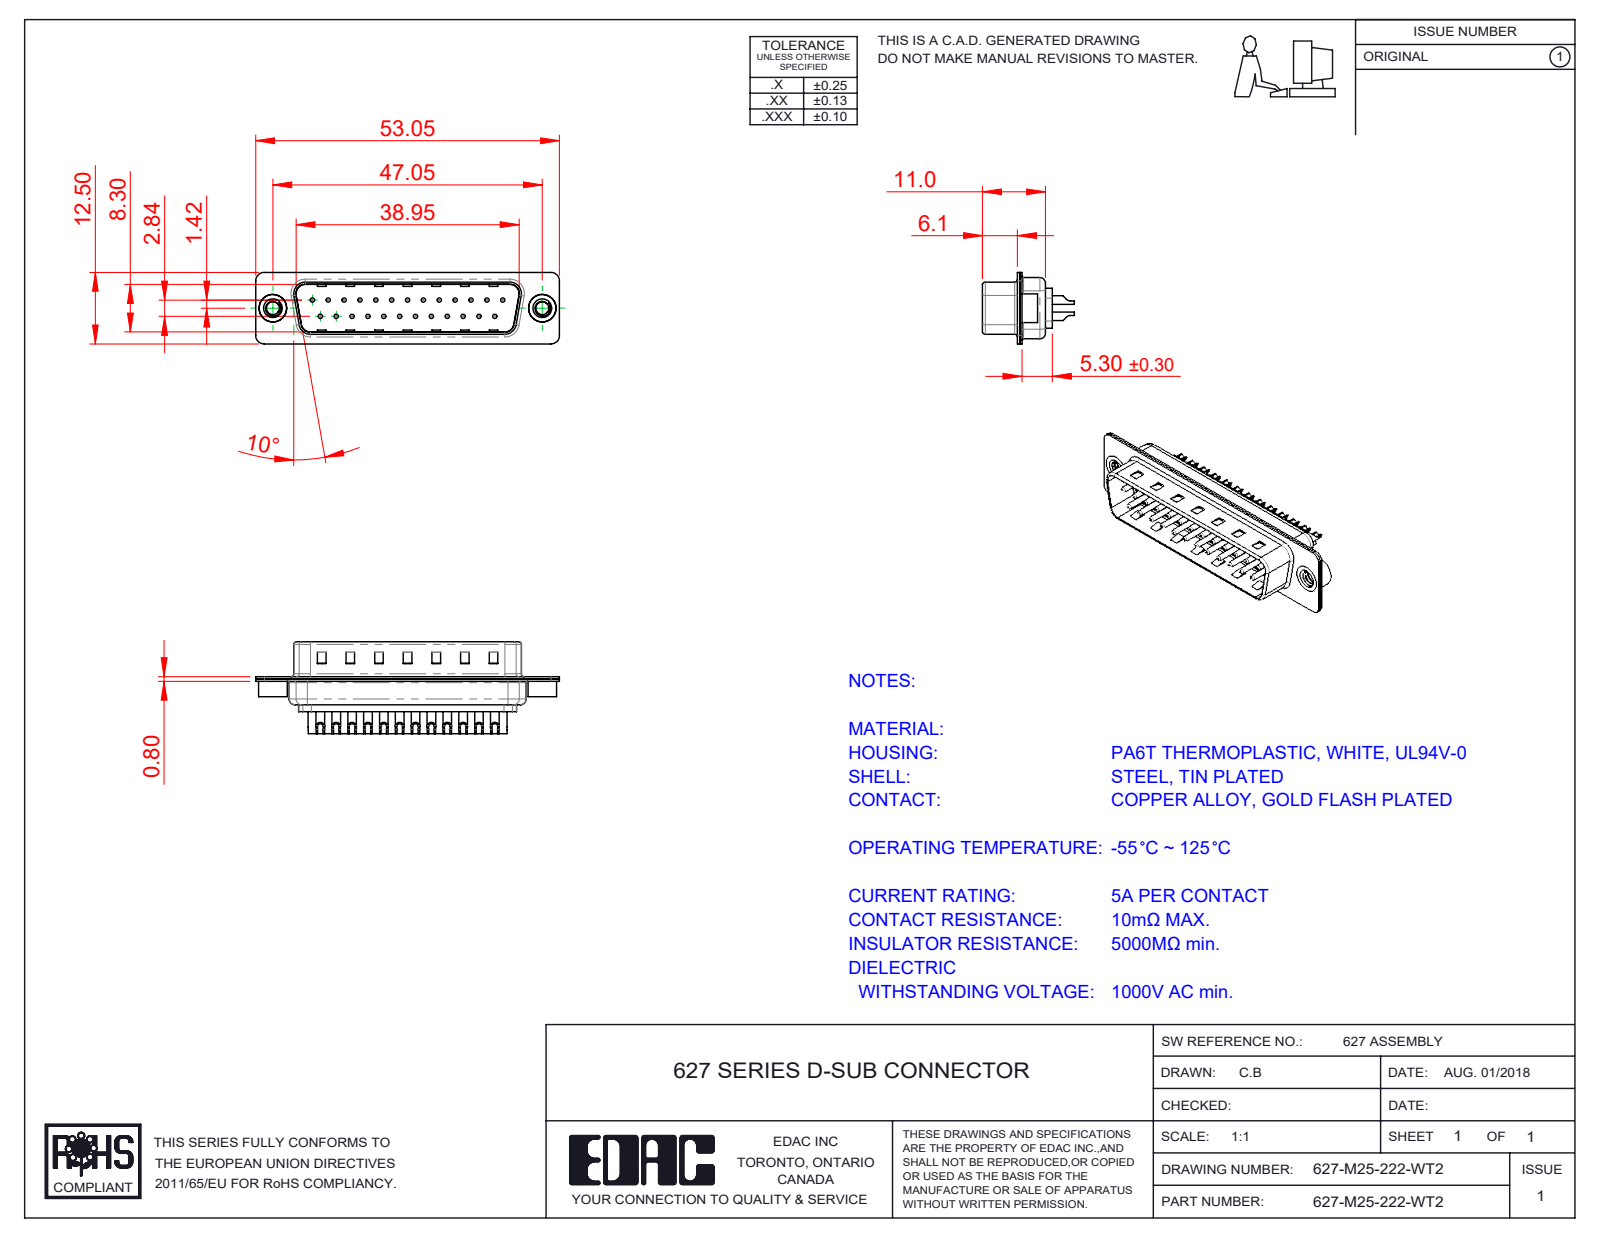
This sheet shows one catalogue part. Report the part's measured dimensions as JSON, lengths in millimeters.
{"part_name": "627M 4-40 Threaded Rivet; 627M Housing_25 Contacts; 627M Shell Rear_25 Contacts; 627M Contact Row 1_22 (+3 more)", "step_written_by": "SolidWorks 2020 (CONFIG_CONTROL_DESIGN)", "units": "millimeters", "bodies": {"solids": 30, "faces": 1301, "planar": 396, "cylindrical": 537, "other": 368}, "overall_size": [53.05, 16.05, 12.5], "volume_mm3": 2776, "surface_area_mm2": 7078, "round_holes": [[0.75, 25], [1, 25], [1.6, 25], [2, 25], [2.26, 2], [4, 2], [4.8, 2]], "round_bosses_or_shafts": [[1.5, 25], [5, 2], [4.9, 2]], "partial_cylinders_radius": [[1.5, 16], [2, 12], [0.5, 8], [1.6, 8], [1, 6], [0.25, 4], [0.6, 4], [0.65, 4]], "face_to_face_distances": [0.4, 0.8, 9.5, 9.1, 8.7, 9.9, 1.2, 0.75, 0.35, 6.1], "hole_center_spacings": [3.16, 2.77, 5.54, 8.31, 11.08, 13.85, 16.62, 5.03]}
